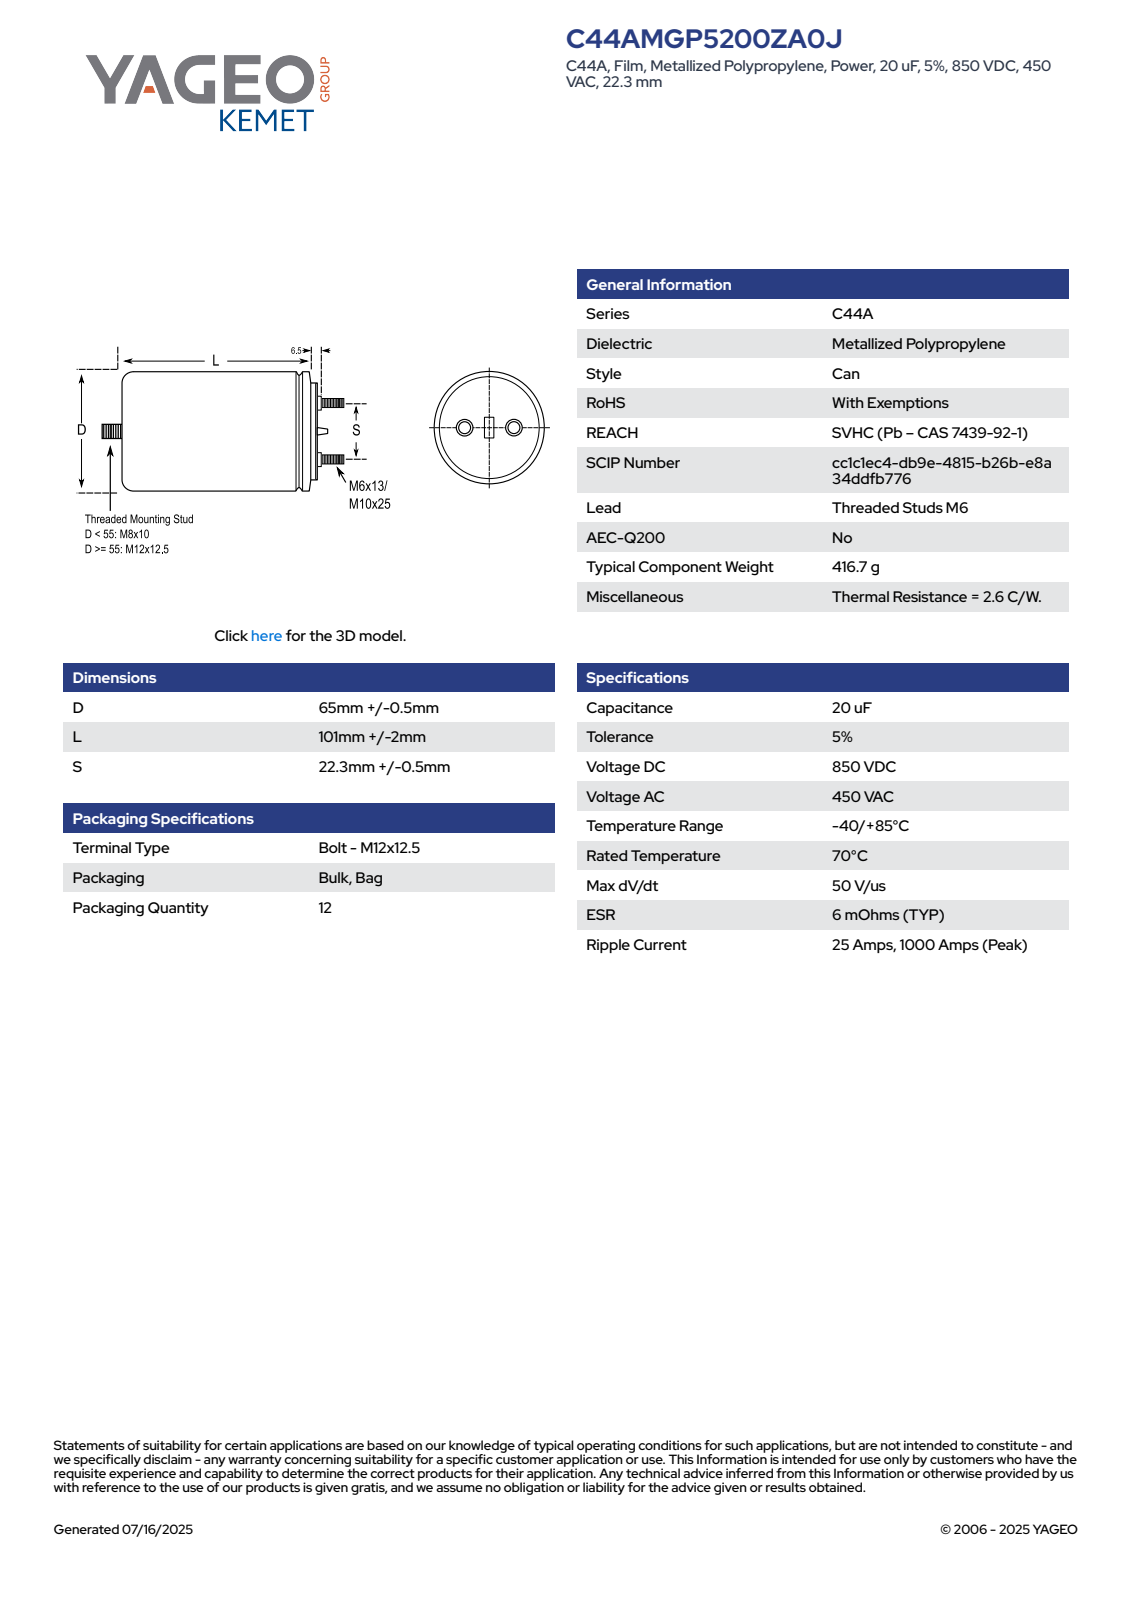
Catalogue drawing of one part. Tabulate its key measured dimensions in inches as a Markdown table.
| quantity | value |
| --- | --- |
| part name | CFP_C44A_65X101_D65.5L103S22.3 |
| STEP written by | SolidWorks 2014 (AUTOMOTIVE_DESIGN) |
| units | inches |
| bodies | 1 solid, 102 faces (29 planar, 34 cylindrical, 39 other) |
| overall size | 5.315 × 2.579 × 2.579 |
| volume | 21.79 in³ |
| surface area | 45.96 in² |
| round bosses / shafts (diameter × count) | 0.354 × 2, 0.236 × 2, 2.579 × 1, 2.022 × 1, 0.472 × 1 |
| partial cylindrical surfaces (radius × count) | 1.289 × 1 |
| main face-to-face distances | 4.252, 0.492, 4.744, 4.803, 4.311, 0.059, 5.315, 4.823, 0.571, 0.512 |
